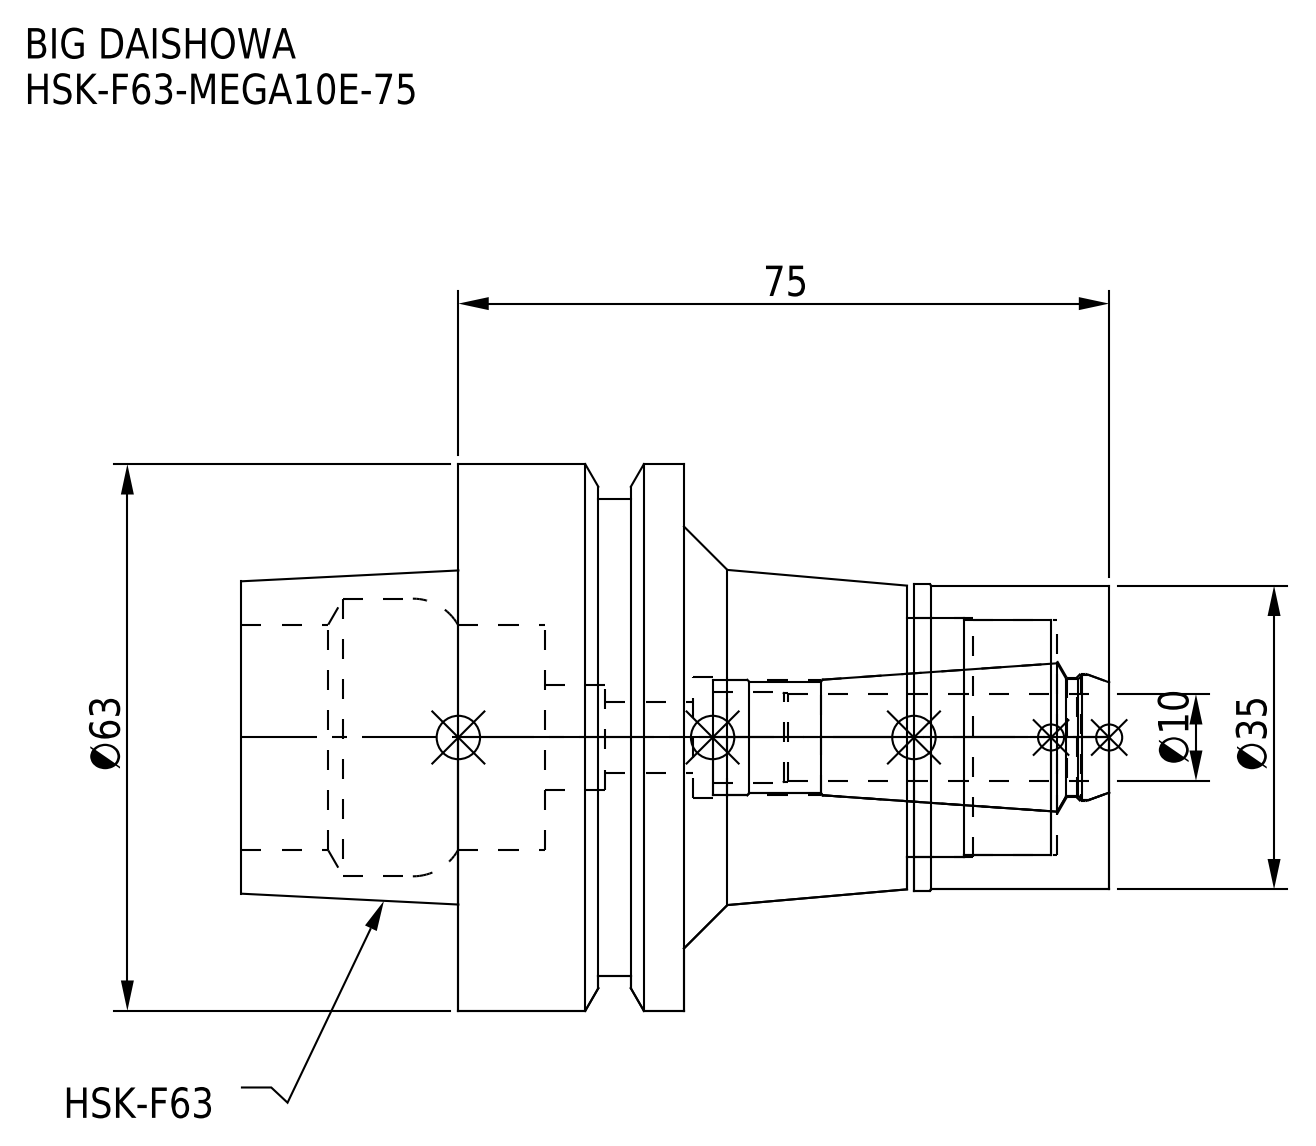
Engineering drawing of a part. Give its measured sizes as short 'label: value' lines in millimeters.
name: HSK-F63-MEGA10E-75; HSK-F63-MEGA10E-75-100.stp; HF63ME10075-100_ASM.stp; HSK-F63-MEGA10E-75-100-FreeParts (+3 more)
written by: SolidWorks 2019 (CONFIG_CONTROL_DESIGN)
unit: mm
bodies: 2 solids, 78 faces (16 planar, 38 cylindrical, 24 other)
size: 100 × 63 × 63
volume: 124 899 mm³; area: 30 399 mm²
holes: 1× ⌀8.25, 1× ⌀12, 1× ⌀13.3, 1× ⌀13.8, 1× ⌀13.9, 1× ⌀14.7, 1× ⌀26, 1× ⌀27, 1× ⌀27.5, 1× ⌀32
bosses: 1× ⌀63, 1× ⌀55, 1× ⌀35.3, 1× ⌀35
face distances: 26, 49, 75, 100, 51, 25, 65.05, 16.05, 9.95, 34.95
